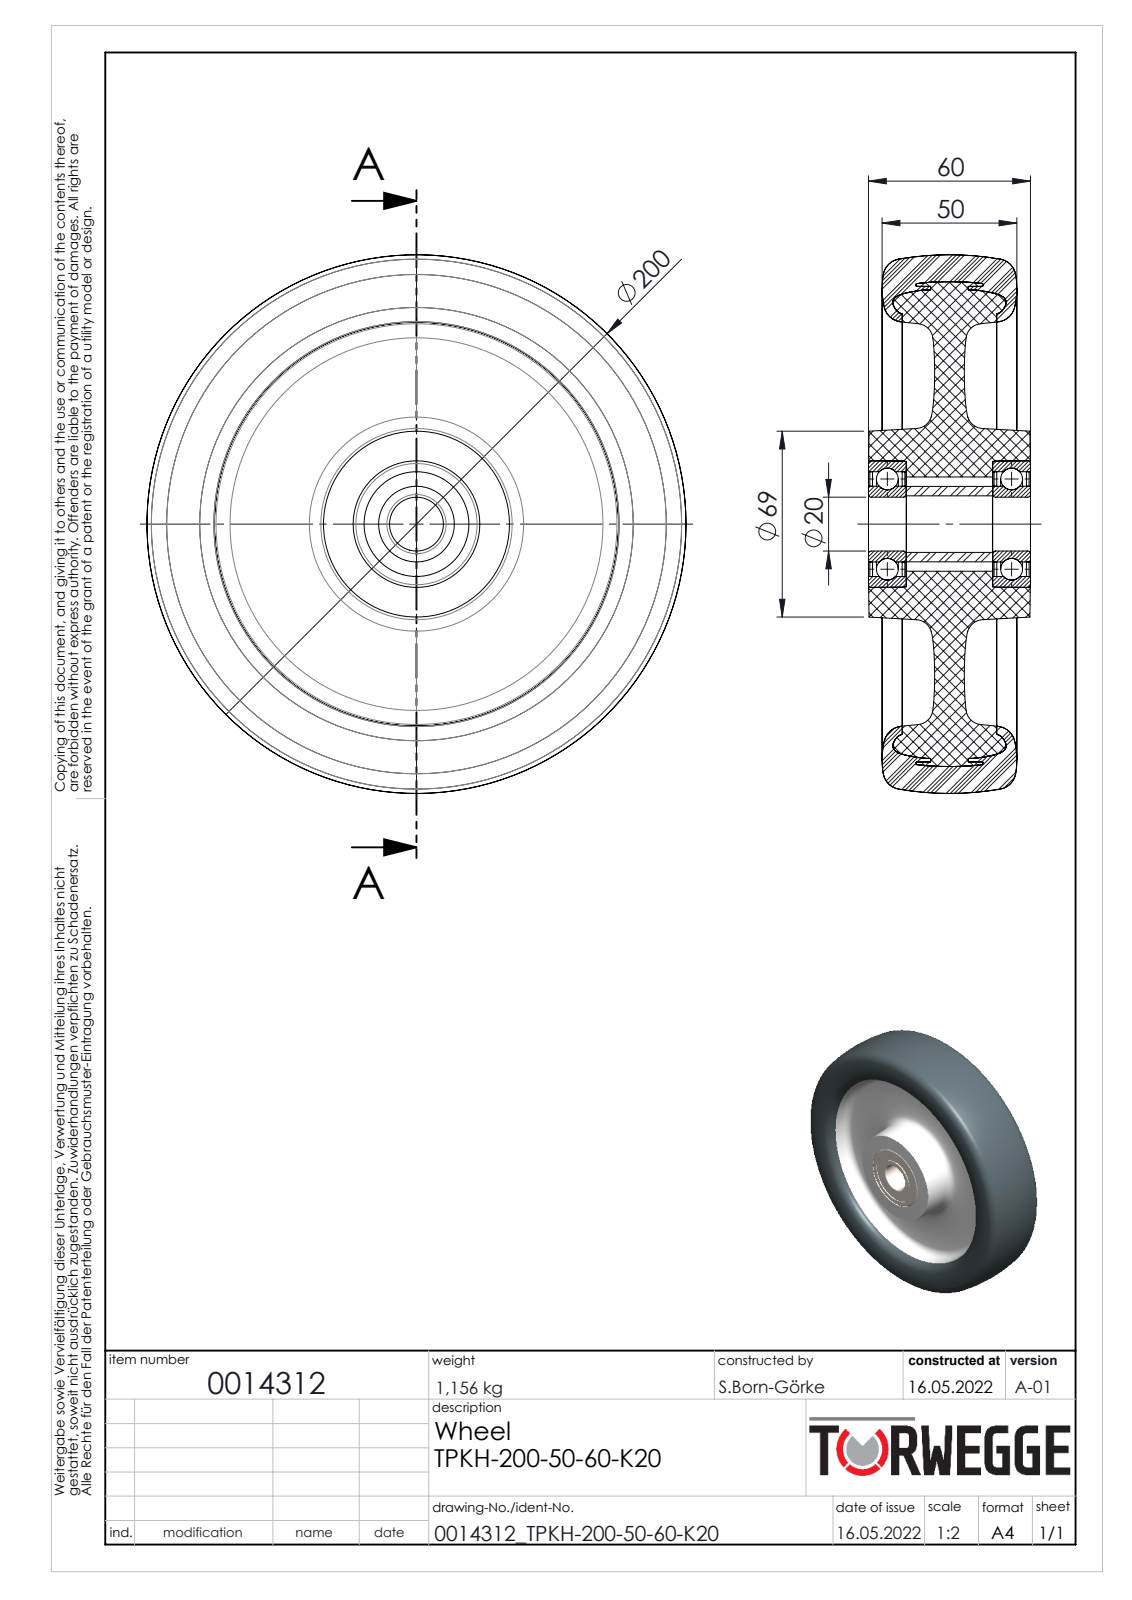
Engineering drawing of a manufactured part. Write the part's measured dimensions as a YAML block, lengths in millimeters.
part_name: "0014312"
step_written_by: "SolidWorks 2020 (AUTOMOTIVE_DESIGN)"
units: millimeters
bodies: {solids: 0, faces: 255, planar: 64, cylindrical: 54, other: 137}
overall_size: [200, 199.97, 60.1]
round_holes:
  - {diameter: 20, count: 1}
  - {diameter: 21, count: 1}
  - {diameter: 28.1, count: 1}
  - {diameter: 35, count: 1}
  - {diameter: 38.9, count: 1}
round_bosses_or_shafts:
  - {diameter: 47, count: 1}
  - {diameter: 28, count: 1}
partial_cylinders:
  - {radius: 87, count: 1}
face_to_face_distances: [1.5, 46.1, 23.05, 33.55, 35, 14, 10.5, 24.5, 12.55, 46.05]
